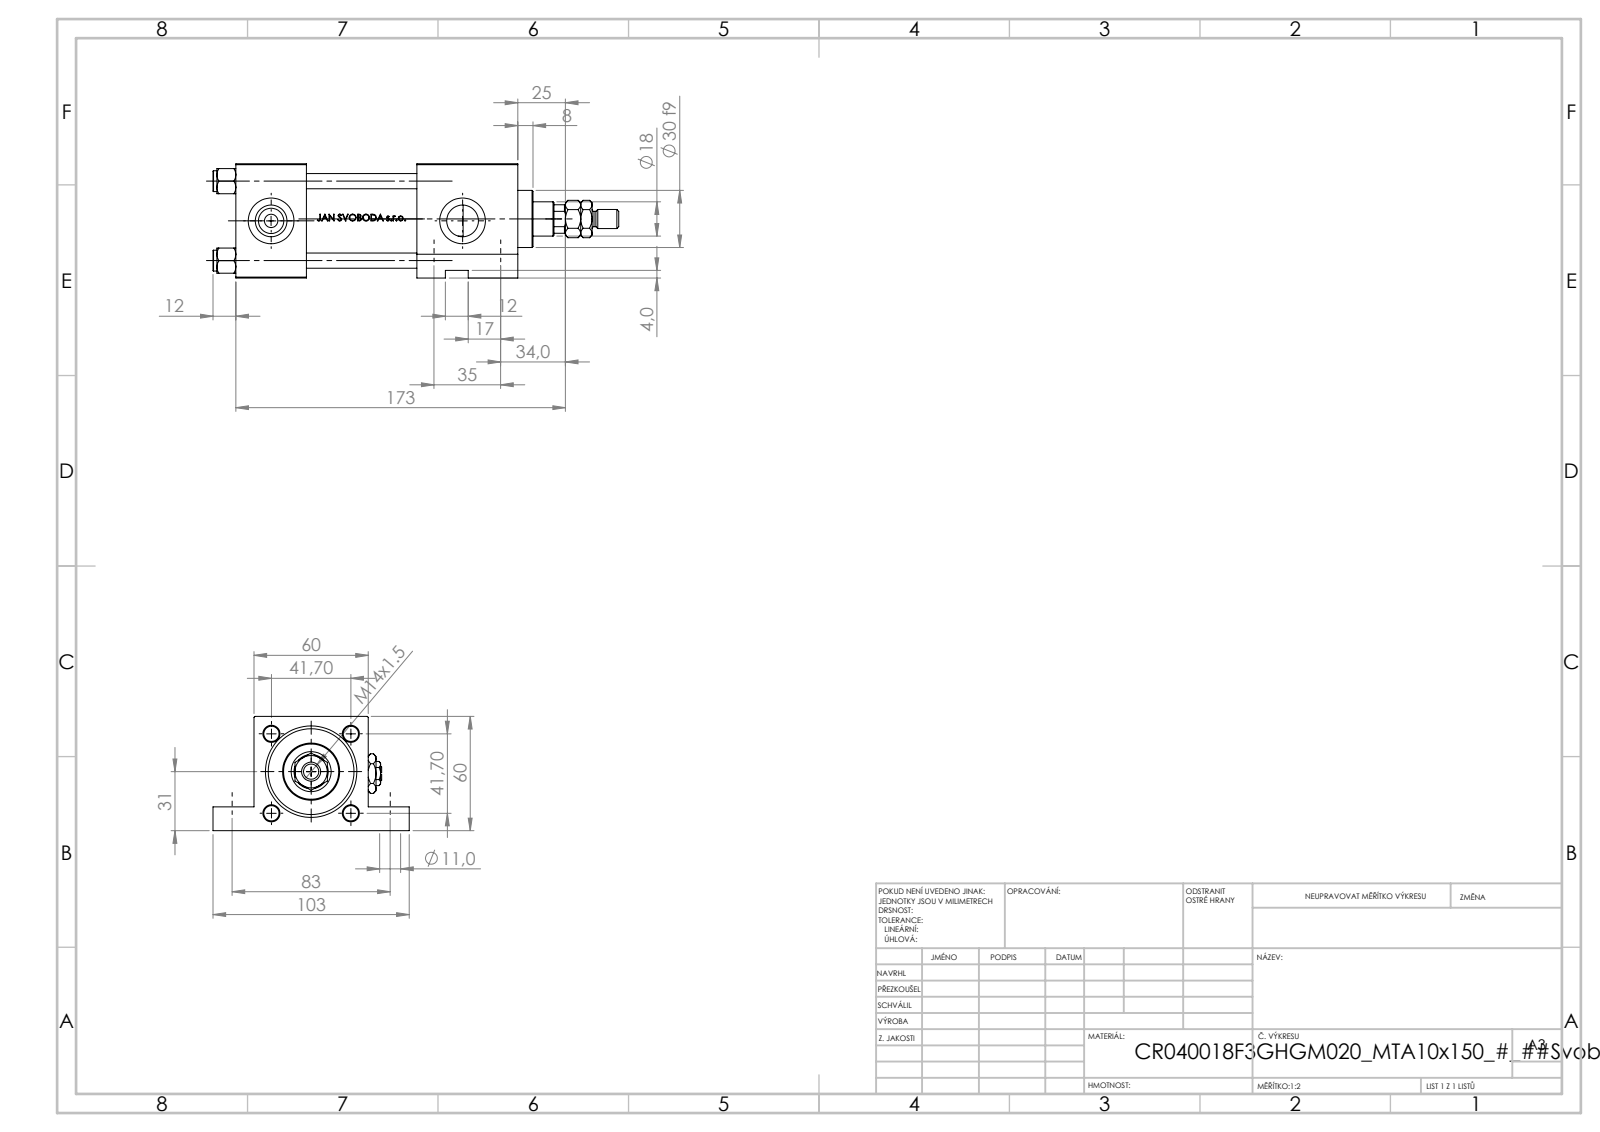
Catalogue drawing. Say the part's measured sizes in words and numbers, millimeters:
The part is named "V215CR_F_TYCINKA; MTA; V215CR_F_Body; Zatka_pro_OIL_PORT (+3 more)". Its 3-D file was written by "SolidWorks 2019 (CONFIG_CONTROL_DESIGN)". It is 14 solids with 1264 faces: 499 planar, 153 cylindrical and 612 other. Overall it measures 213 by 103 by 60 millimeters. Its volume is 424 634 cubic millimeters and its surface area 116 261 square millimeters. Round holes: 4 of diameter 8, 3 of diameter 16.66, 3 of diameter 24, 2 of diameter 7, 2 of diameter 11, 2 of diameter 11, 1 of diameter 8.5, 1 of diameter 16, 1 of diameter 18, 1 of diameter 21, 1 of diameter 31, 1 of diameter 40. Round bosses or shafts: 4 of diameter 11, 1 of diameter 46, 1 of diameter 30, 1 of diameter 10, 1 of diameter 8. Partial cylindrical surfaces (rounded edges, fillets, slot ends): 1 of radius 8.5. The main face-to-face distances are 60, 37, 148, 111, 53, 58, 95, 119.3, 82.3, 24.3. The hole center spacings are 41.7, 28.79, 30.2, 35, 58.97, 83, 90.08, 8.
